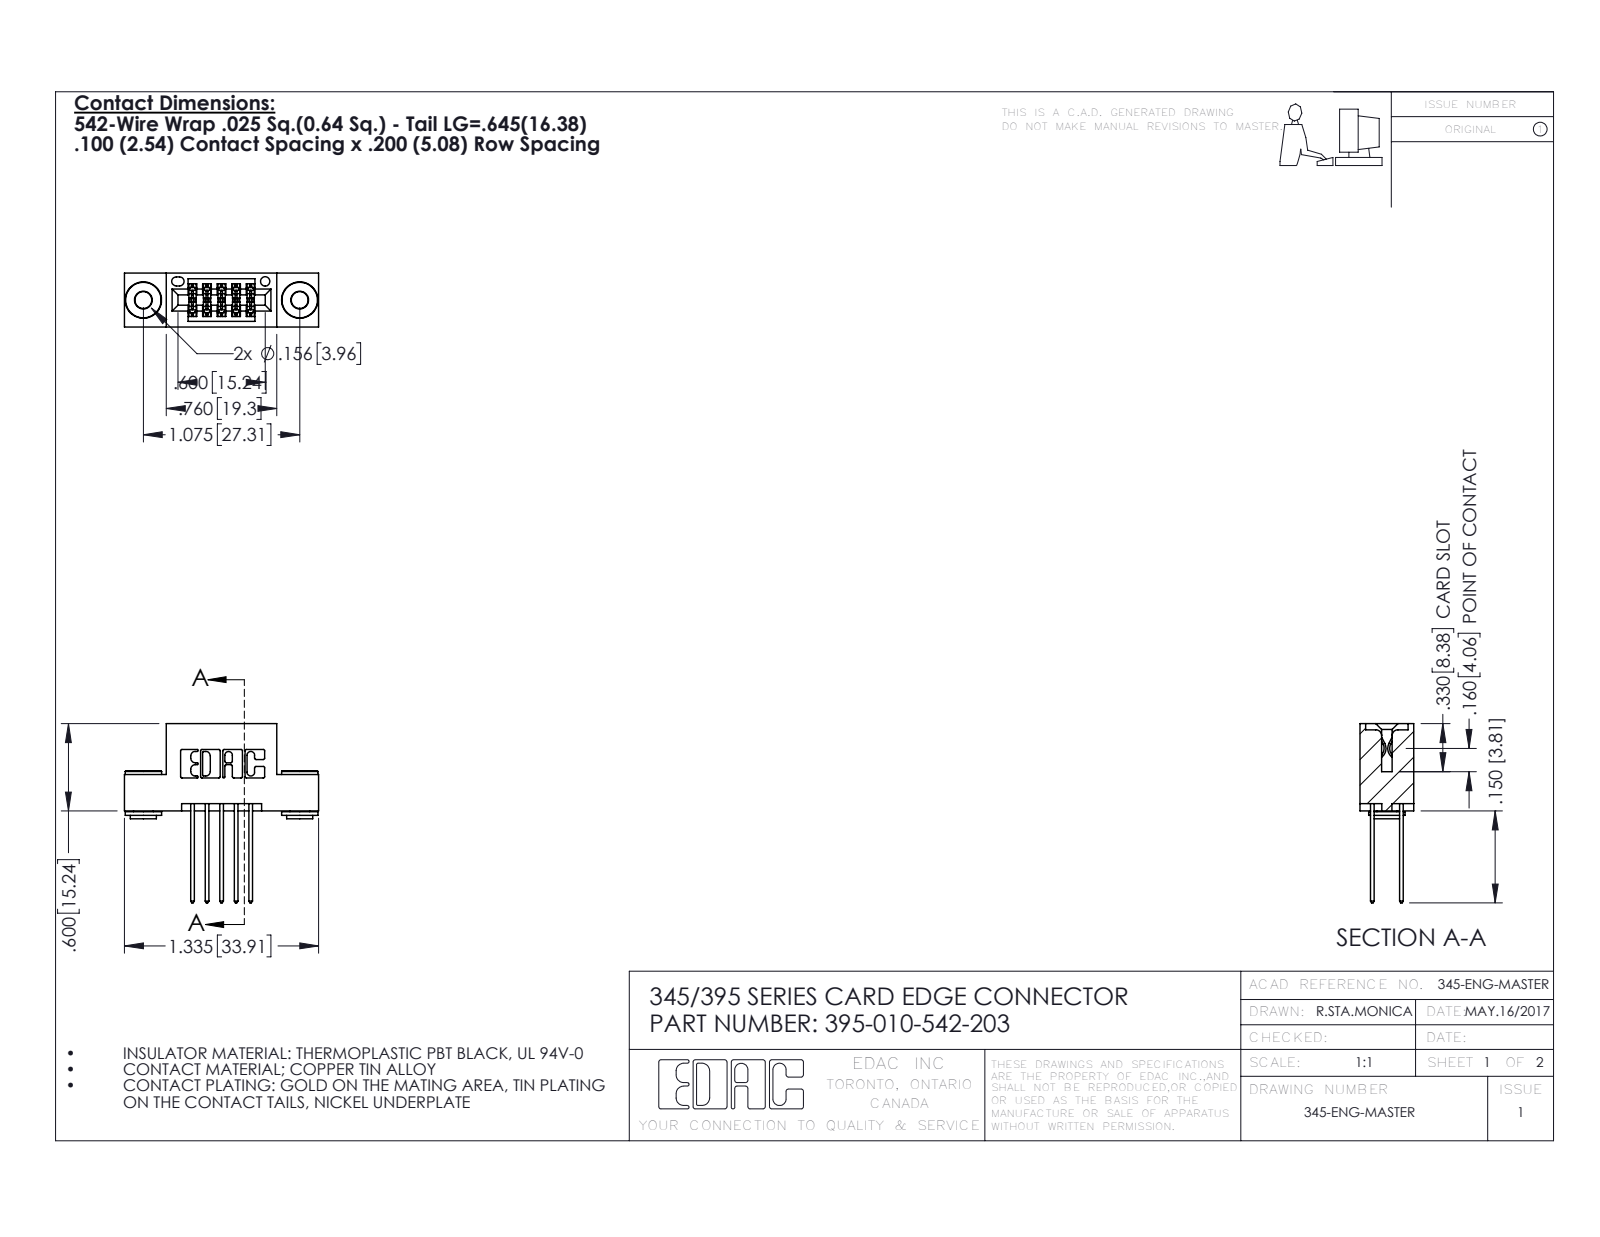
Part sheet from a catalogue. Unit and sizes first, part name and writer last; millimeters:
Units: millimetres
Overall size (bounding box): 33.9 × 31.3 × 9.4
Round holes (diameter × count): ⌀2.9 ×2, ⌀4 ×2, ⌀1.6 ×1
Round bosses / shafts (diameter × count): ⌀6.4 ×2, ⌀4.6 ×2, ⌀3.5 ×2
Partial cylindrical surfaces — rounded edges, fillets, slot ends (radius × count): R0.3 ×22, R0.2 ×15, R0.3 ×10, R0.2 ×6, R0.8 ×6, R0.7 ×3, R0.4 ×2, R0.5 ×2
Main face-to-face distances: 5.1, 1.8, 7.6, 2.5, 9.4, 0.6, 2.5, 6.9, 5.7, 6.4
Hole centre spacings: 6.9, 21.5, 27.3
Volume: 3 020 mm³ · Surface area: 4 165 mm²
Bodies: 13 solids, 664 faces (420 planar, 236 cylindrical, 8 other)
Part name (STEP PRODUCT): 395-010-542-203; 345-250-002_345-250-002-102; 345 Part_Flush Mounting Lugs - 0.156 Dia-TH; 345-292-001_345-293-142
STEP written by: SolidWorks 2016 (CONFIG_CONTROL_DESIGN)
